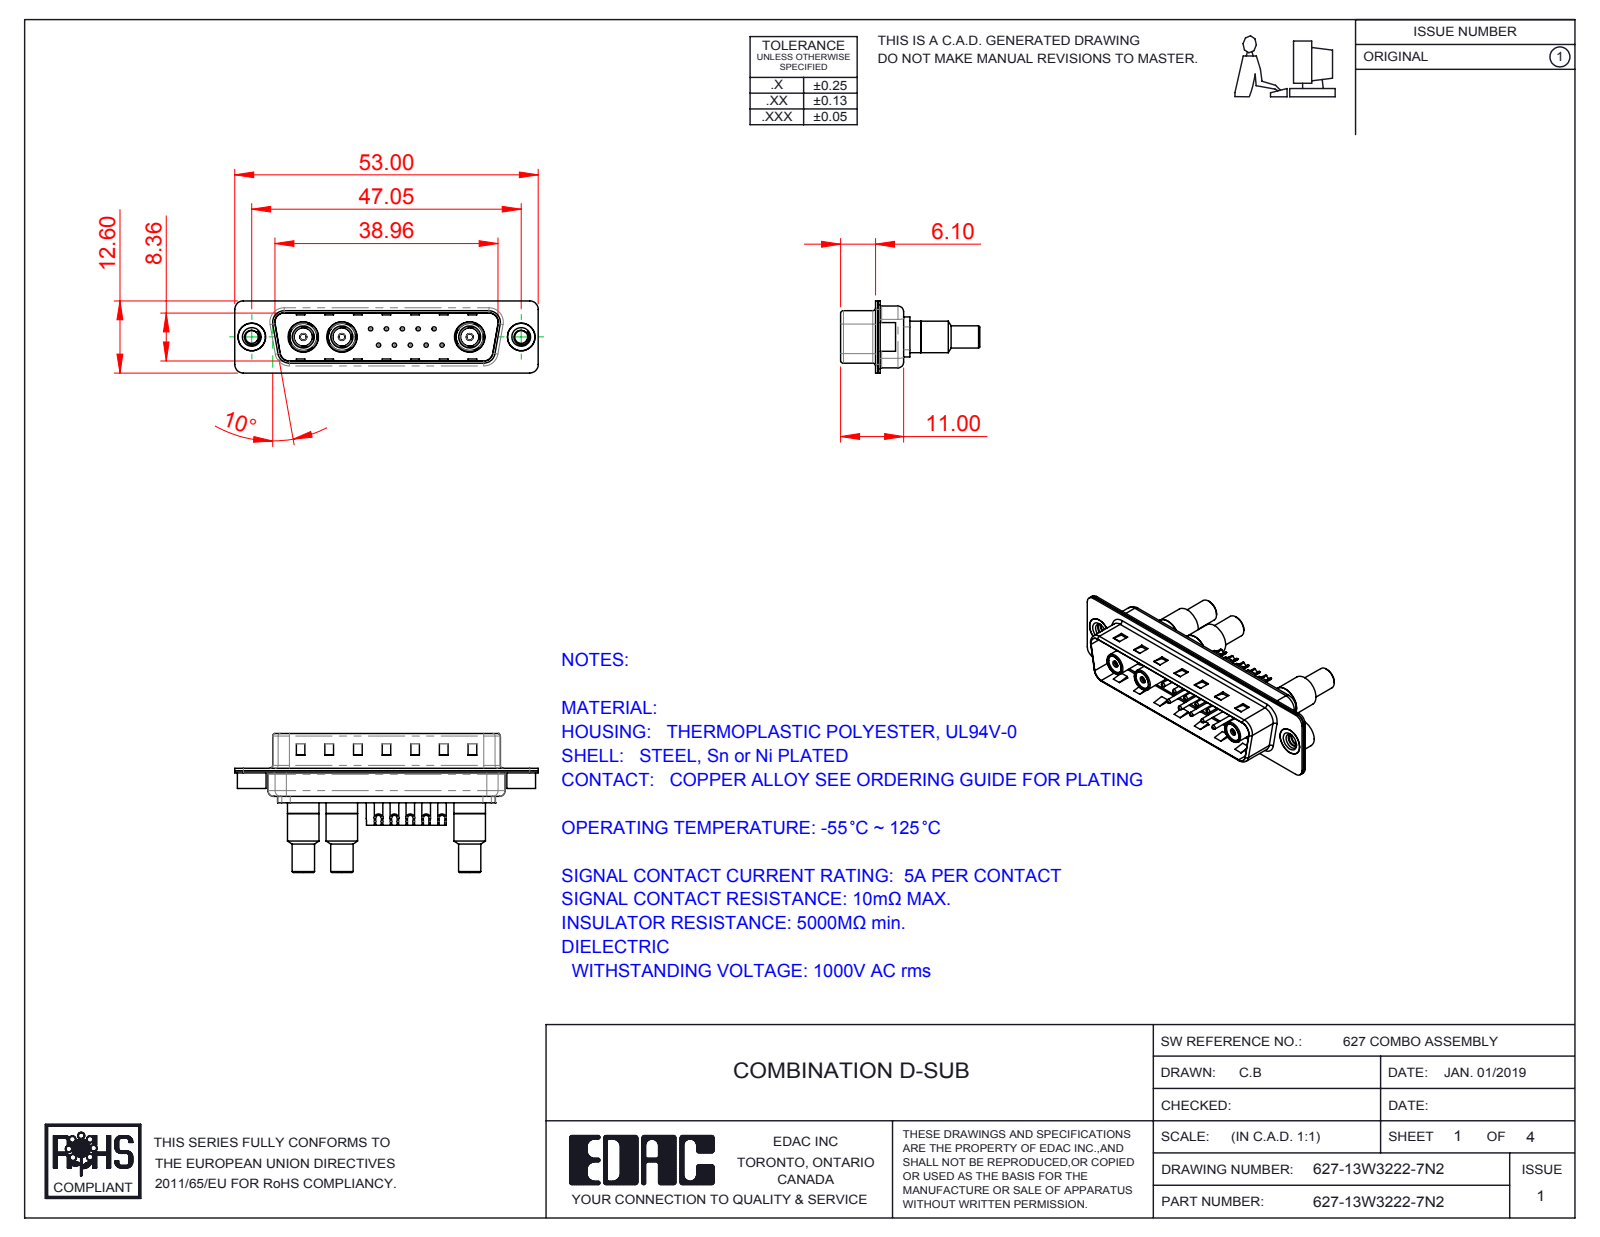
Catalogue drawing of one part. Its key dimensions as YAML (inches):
part_name: "627Combo Contact Row 1_22; Co-Ax Jack Assy_SC; Solder Cover; Socket_Solder Cup (+8 more)"
step_written_by: "SolidWorks 2016 (CONFIG_CONTROL_DESIGN)"
units: inches
bodies: {solids: 33, faces: 1136, planar: 381, cylindrical: 489, other: 266}
overall_size: [2.087, 0.957, 0.496]
volume: 0.19
surface_area: 14.47
round_holes:
  - {diameter: 0.063, count: 13}
  - {diameter: 0.03, count: 10}
  - {diameter: 0.039, count: 10}
  - {diameter: 0.079, count: 10}
  - {diameter: 0.189, count: 5}
  - {diameter: 0.031, count: 3}
  - {diameter: 0.043, count: 3}
  - {diameter: 0.047, count: 3}
  - {diameter: 0.059, count: 3}
  - {diameter: 0.071, count: 3}
  - {diameter: 0.098, count: 3}
  - {diameter: 0.106, count: 3}
round_bosses_or_shafts:
  - {diameter: 0.059, count: 10}
  - {diameter: 0.217, count: 3}
  - {diameter: 0.205, count: 3}
  - {diameter: 0.187, count: 3}
  - {diameter: 0.186, count: 3}
  - {diameter: 0.154, count: 3}
  - {diameter: 0.152, count: 3}
  - {diameter: 0.148, count: 3}
partial_cylinders:
  - {radius: 0.059, count: 17}
  - {radius: 0.079, count: 12}
  - {radius: 0.02, count: 8}
  - {radius: 0.063, count: 8}
  - {radius: 0.039, count: 6}
  - {radius: 0.01, count: 4}
  - {radius: 0.024, count: 4}
  - {radius: 0.026, count: 4}
face_to_face_distances: [0.016, 0.032, 0.377, 0.345, 0.236, 0.031, 0.059, 0.048, 0.393, 0.017]
hole_center_spacings: [0.124, 0.109, 0.198, 0.218, 0.295, 0.198, 0.327, 0.398]
